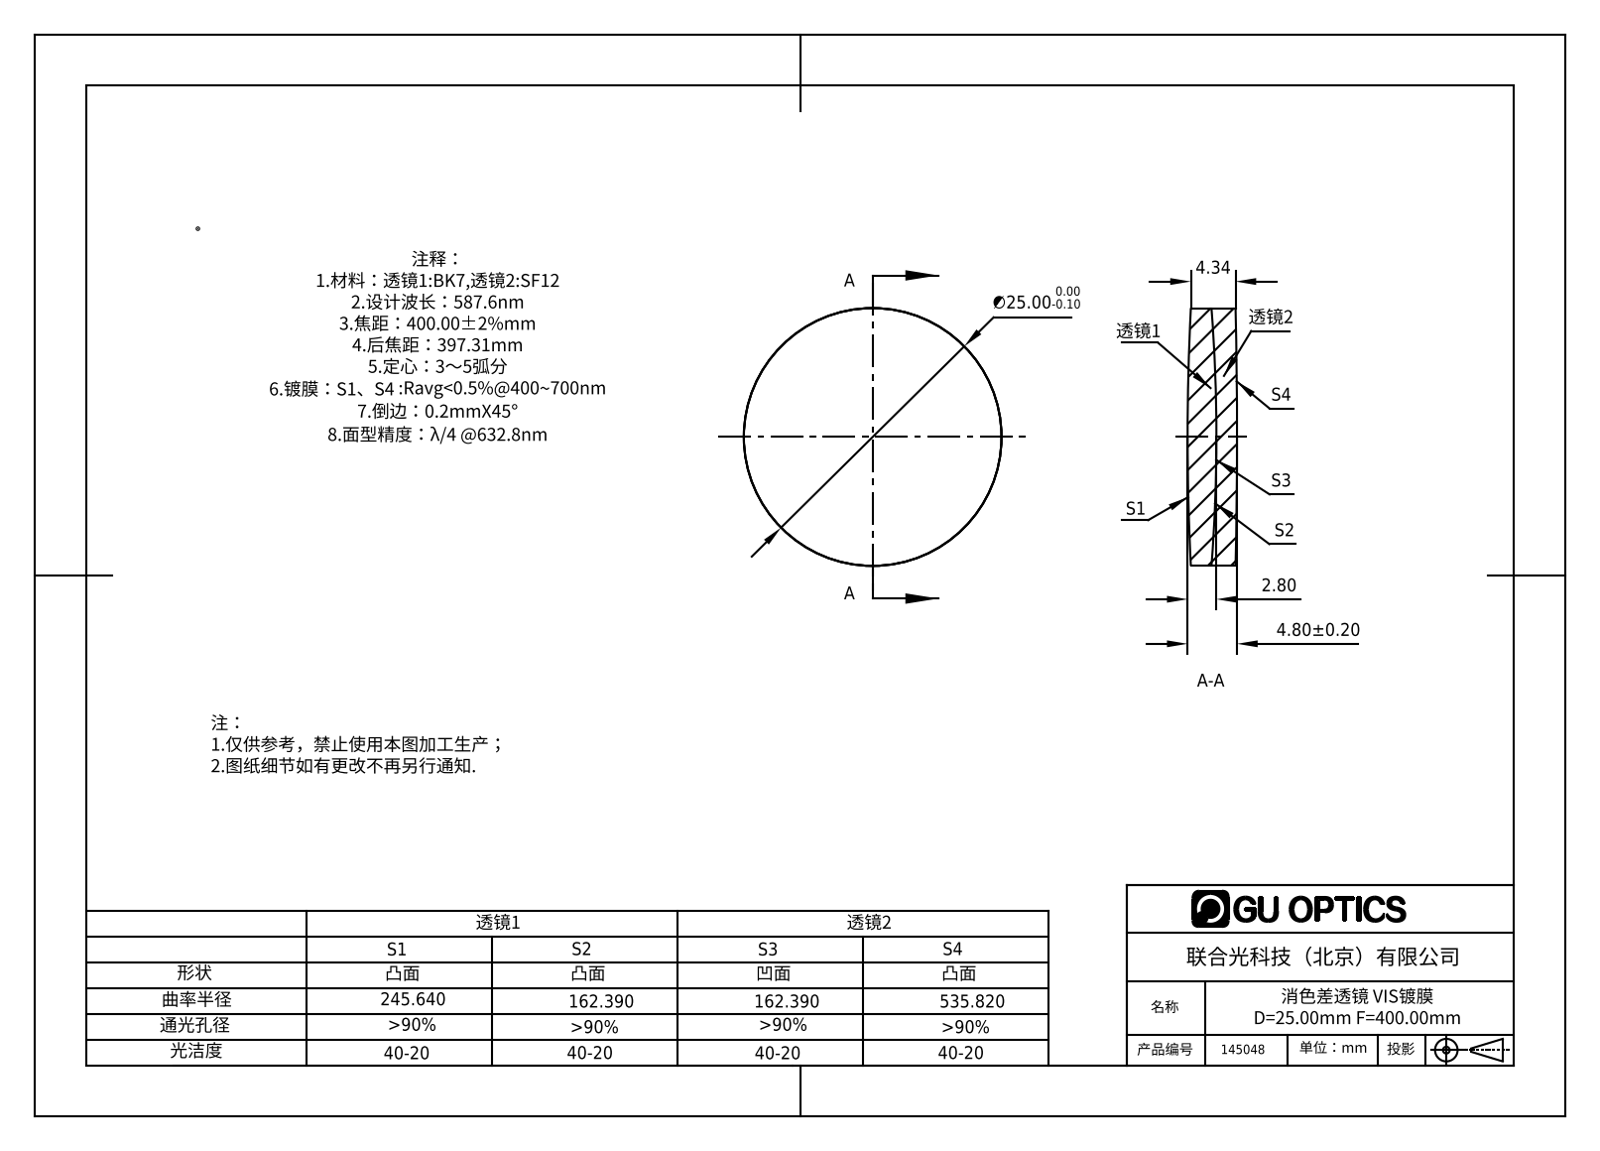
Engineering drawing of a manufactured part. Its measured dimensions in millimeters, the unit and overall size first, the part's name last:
Units: millimetres
Overall size (bounding box): 25 × 25 × 4.8
Round bosses / shafts (diameter × count): ⌀25 ×1
Volume: 2 242 mm³ · Surface area: 2 306 mm²
Bodies: 2 solids, 12 faces (0 planar, 4 cylindrical, 8 other)
Part name (STEP PRODUCT): 145048
STEP written by: SolidWorks 2016 (AUTOMOTIVE_DESIGN)
